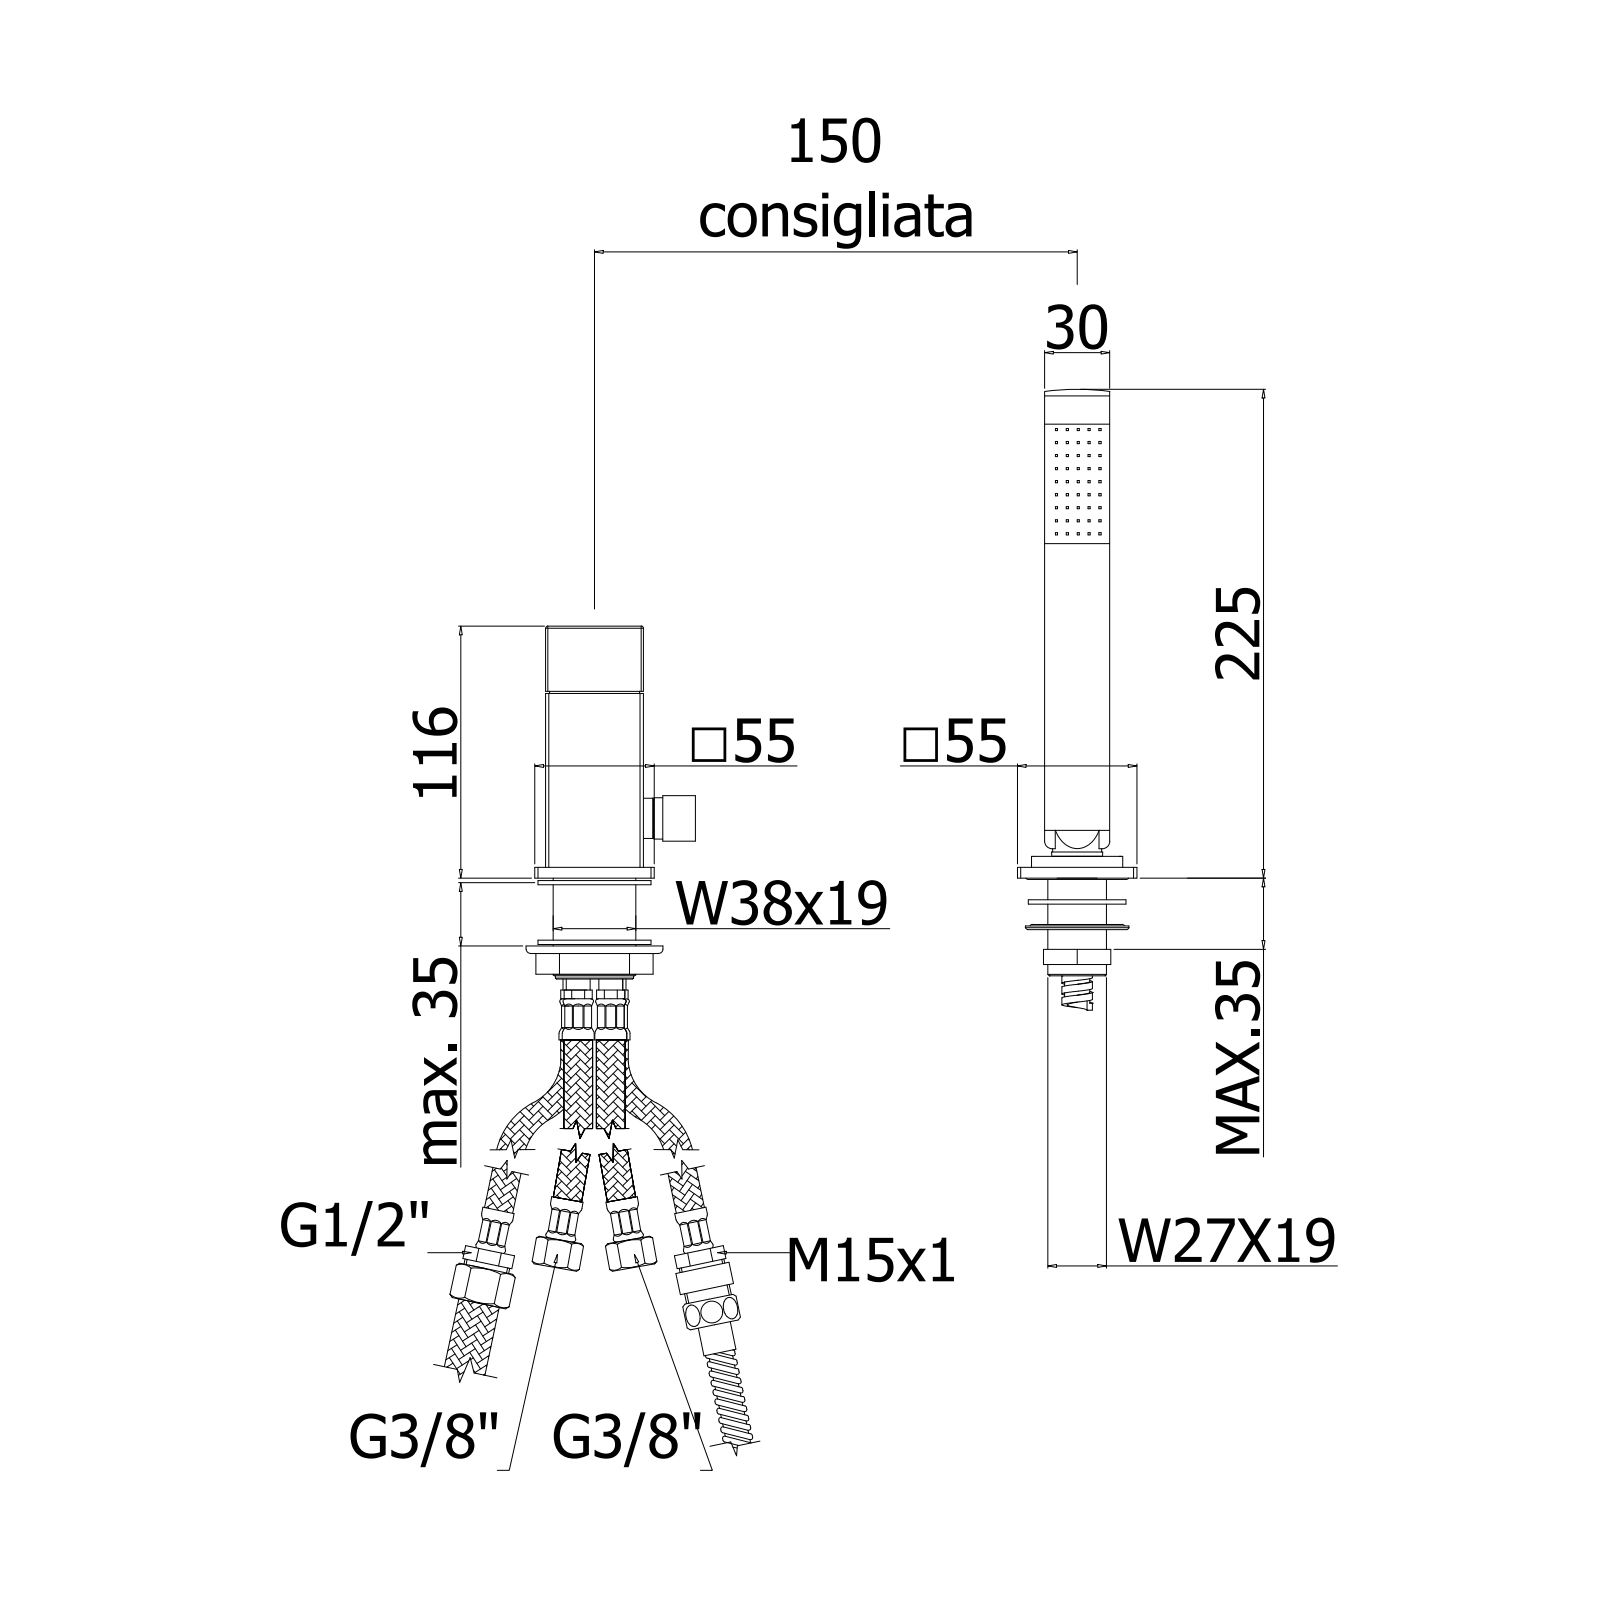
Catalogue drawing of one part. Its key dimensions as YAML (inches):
part_name: "LEC041CR"
step_written_by: "CREO PARAMETRIC BY PTC INC, 2020044 (CONFIG_CONTROL_DESIGN)"
units: inches
bodies: {solids: 4, faces: 1449, planar: 892, cylindrical: 348, other: 209}
overall_size: [8.78, 8.071, 2.165]
volume: 15.93
surface_area: 153.4
round_holes:
  - {diameter: 0.276, count: 7}
  - {diameter: 0.157, count: 2}
  - {diameter: 1.89, count: 2}
  - {diameter: 0.122, count: 1}
  - {diameter: 0.13, count: 1}
  - {diameter: 0.165, count: 1}
  - {diameter: 0.169, count: 1}
  - {diameter: 0.177, count: 1}
  - {diameter: 0.197, count: 1}
  - {diameter: 0.283, count: 1}
  - {diameter: 0.354, count: 1}
  - {diameter: 0.374, count: 1}
round_bosses_or_shafts:
  - {diameter: 0.079, count: 11}
  - {diameter: 1.673, count: 2}
  - {diameter: 0.709, count: 2}
  - {diameter: 0.591, count: 2}
  - {diameter: 1.654, count: 1}
  - {diameter: 1.575, count: 1}
  - {diameter: 1.496, count: 1}
  - {diameter: 1.378, count: 1}
partial_cylinders:
  - {radius: 0.02, count: 27}
  - {radius: 0.006, count: 11}
  - {radius: 0.039, count: 10}
  - {radius: 0.059, count: 8}
  - {radius: 0.012, count: 4}
  - {radius: 0.157, count: 2}
  - {radius: 0.118, count: 1}
  - {radius: 0.154, count: 1}
face_to_face_distances: [1.083, 0.689, 1.772, 0.394, 0.197, 0.118, 1.181, 4.394, 5.61, 6.201]
hole_center_spacings: [0.118, 0.339, 0.419, 0.551, 0.564, 0.555, 2.335, 5.633]
